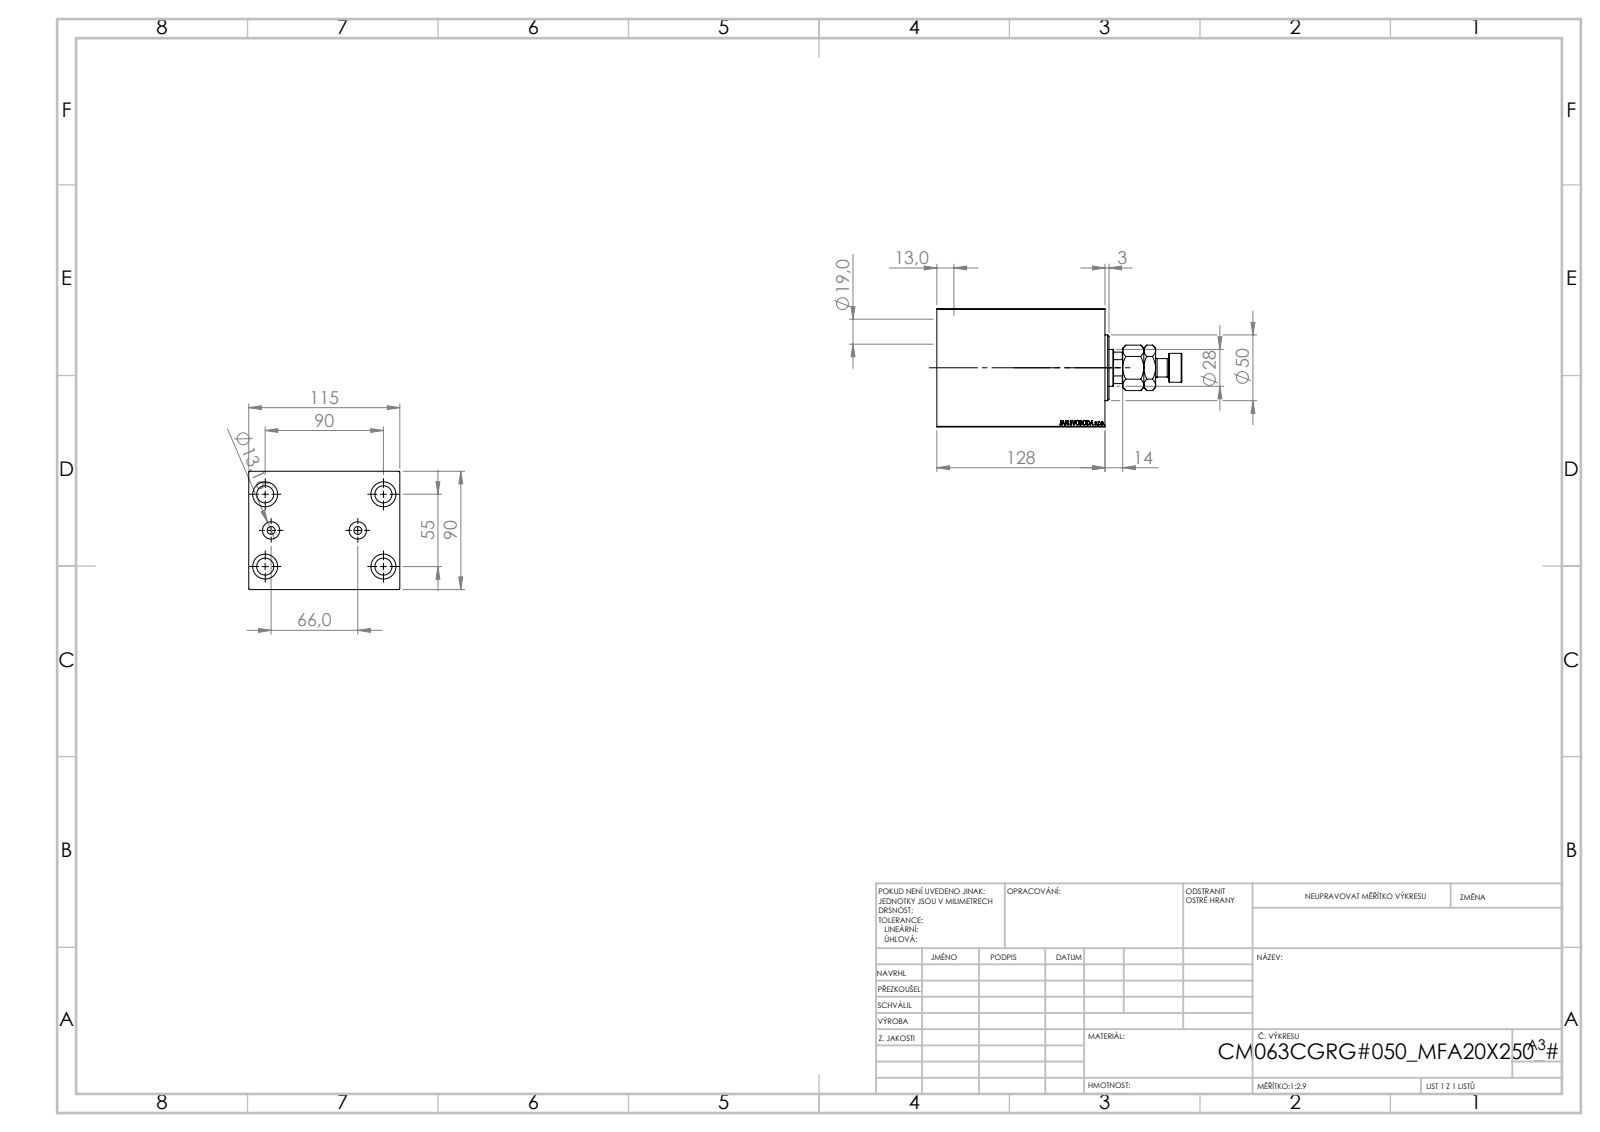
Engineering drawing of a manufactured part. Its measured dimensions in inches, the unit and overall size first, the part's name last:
Units: inches
Overall size (bounding box): 7.343 × 4.528 × 3.543
Round holes (diameter × count): ⌀0.512 ×4, ⌀0.748 ×4, ⌀0.236 ×2, ⌀0.518 ×2, ⌀0.728 ×1, ⌀1.102 ×1, ⌀1.24 ×1, ⌀2.48 ×1, ⌀2.559 ×1, ⌀2.835 ×1
Round bosses / shafts (diameter × count): ⌀1.969 ×1, ⌀0.866 ×1, ⌀0.551 ×1
Partial cylindrical surfaces — rounded edges, fillets, slot ends (radius × count): R0.531 ×1
Main face-to-face distances: 3.543, 4.528, 5.039, 1.909, 3.13, 4.646, 0.394, 2.736, 0.197, 0.768
Hole centre spacings: 1.181, 2.076, 3.256, 1.299, 2.165, 3.543, 4.153, 2.598
Volume: 69.32 in³ · Surface area: 229.7 in²
Bodies: 4 solids, 913 faces (425 planar, 62 cylindrical, 426 other)
Part name (STEP PRODUCT): MFA; V450CM_VC_B; V450CM_C_Body; V450CM_C_VCP
STEP written by: SolidWorks 2019 (CONFIG_CONTROL_DESIGN)
